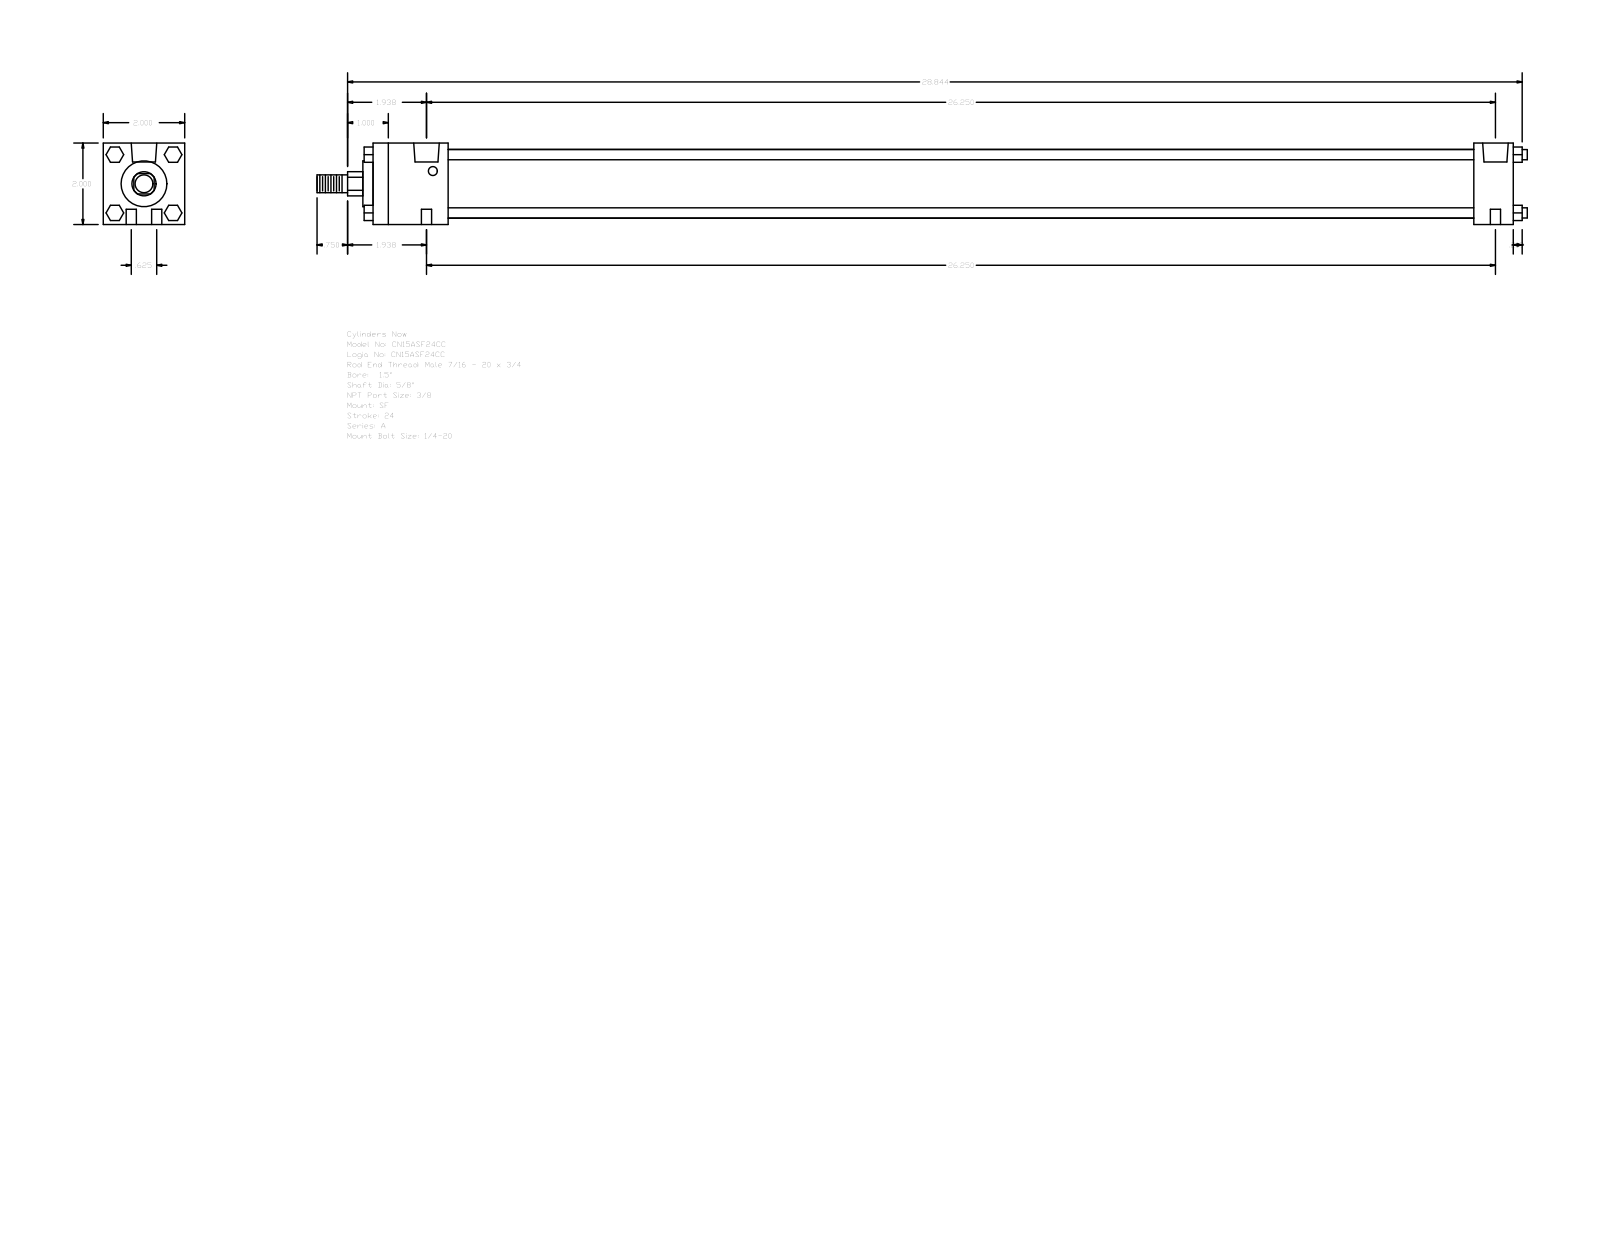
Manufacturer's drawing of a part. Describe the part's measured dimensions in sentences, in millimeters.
The part is named "A_SF__0150_0.625". Its 3-D file was written by "GSSL Pune (CONFIG_CONTROL_DESIGN)". It is 0 solids with 124 faces: 94 planar, 30 cylindrical and 0 other. Overall it measures 754.86 by 50.8 by 50.8 millimeters. Round holes: 4 of diameter 6.35, 2 of diameter 5.56, 2 of diameter 15.93. Round bosses or shafts: 4 of diameter 6.35, 1 of diameter 42.93, 1 of diameter 28.57, 1 of diameter 15.88, 1 of diameter 11.11. Partial cylindrical surfaces (rounded edges, fillets, slot ends): 1 of radius 7.54. The main face-to-face distances are 50.8, 711.2, 46.83, 686.59, 639.76, 664.37, 24.61, 6.35, 9.52, 53.18. The hole center spacings are 7.94, 666.8, 666.75, 15.88, 666.94, 658.81.
